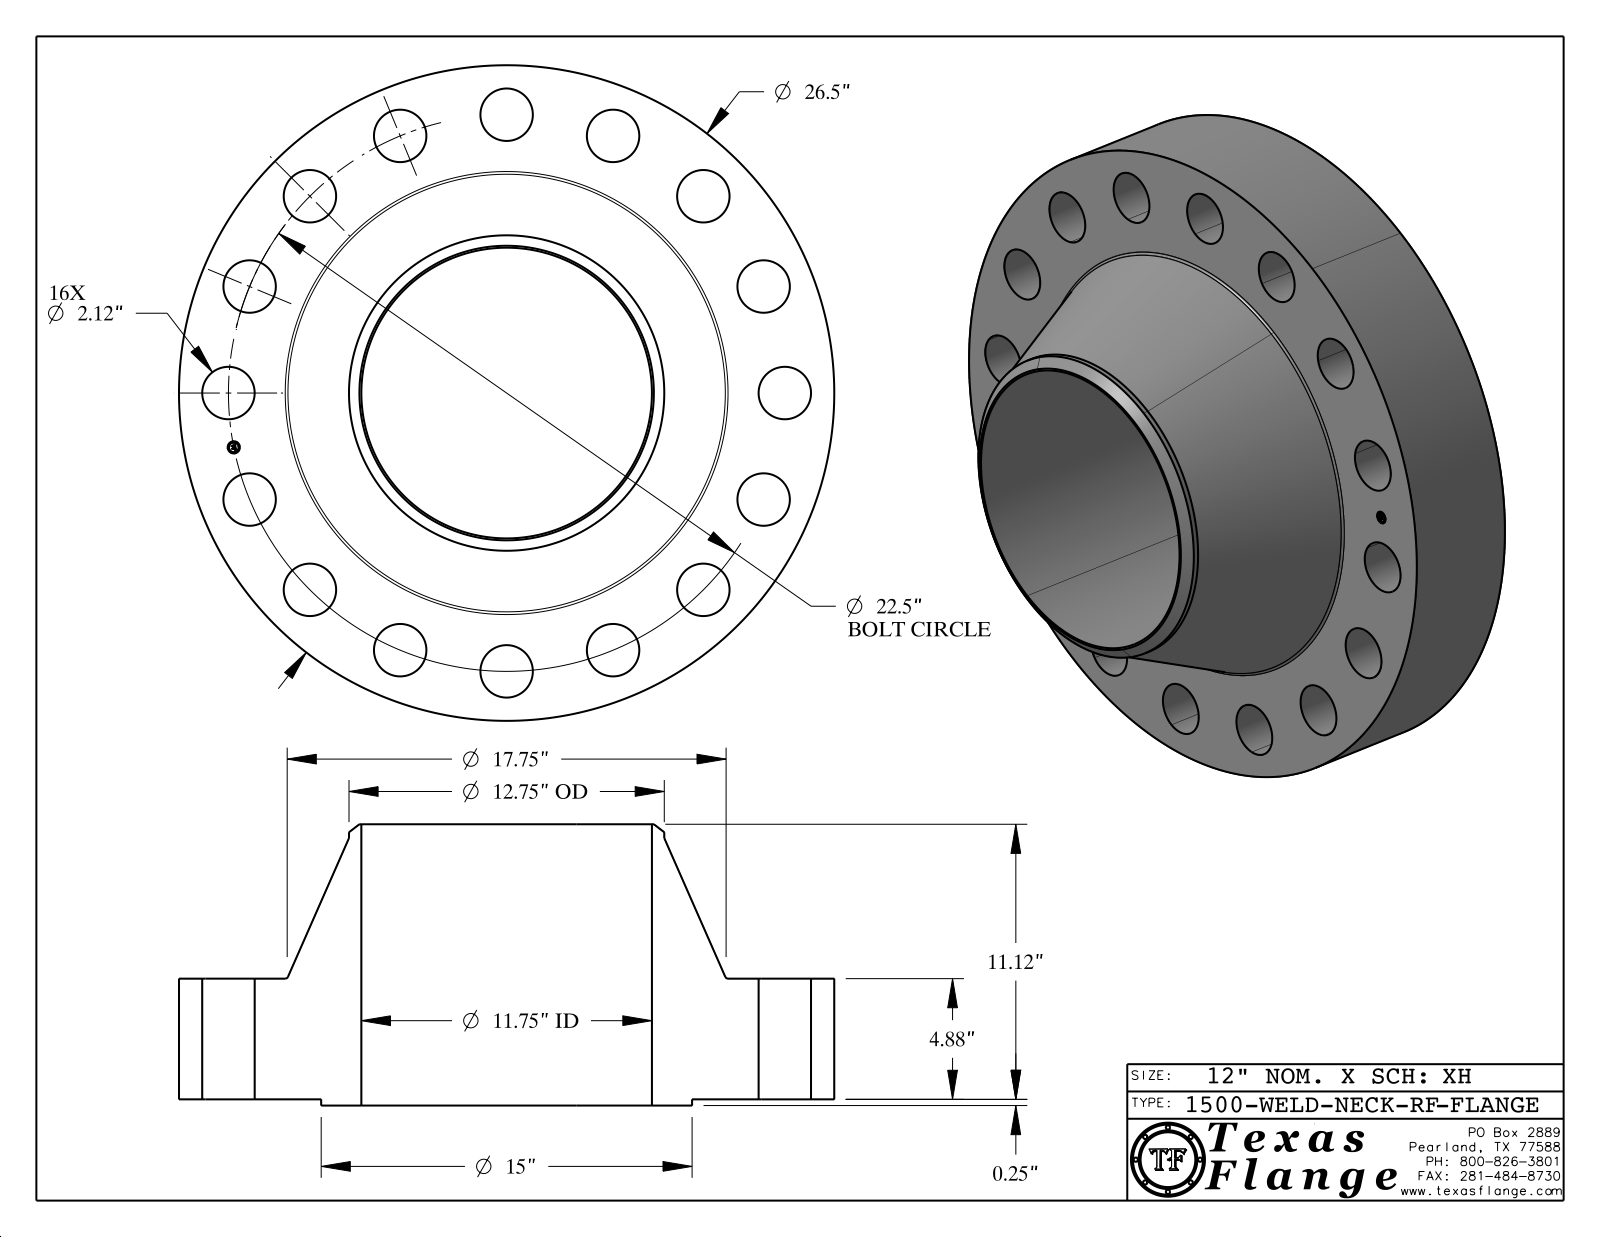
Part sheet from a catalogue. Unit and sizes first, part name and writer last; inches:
Units: inches
Overall size (bounding box): 26.5 × 26.5 × 11.37
Round holes (diameter × count): ⌀2.12 ×16, ⌀0.495 ×1, ⌀11.75 ×1
Round bosses / shafts (diameter × count): ⌀0.03 ×8, ⌀26.5 ×1, ⌀15 ×1, ⌀12.75 ×1, ⌀0.39 ×1
Main face-to-face distances: 4.88, 0.25, 5.13, 11.37, 11.12, 6.24, 5.115, 4.865, 0.015, 6.255
Hole centre spacings: 12.5, 20.787, 22.068, 11.25, 8.611, 15.91, 4.389, 4.39
Volume: 2 343 in³ · Surface area: 2 321 in²
Bodies: 1 solid, 435 faces (369 planar, 60 cylindrical, 6 other)
Part name (STEP PRODUCT): 1500-WELD-NECK-RF
STEP written by: CATIA V5 STEP AP214 (AUTOMOTIVE_DESIGN)
